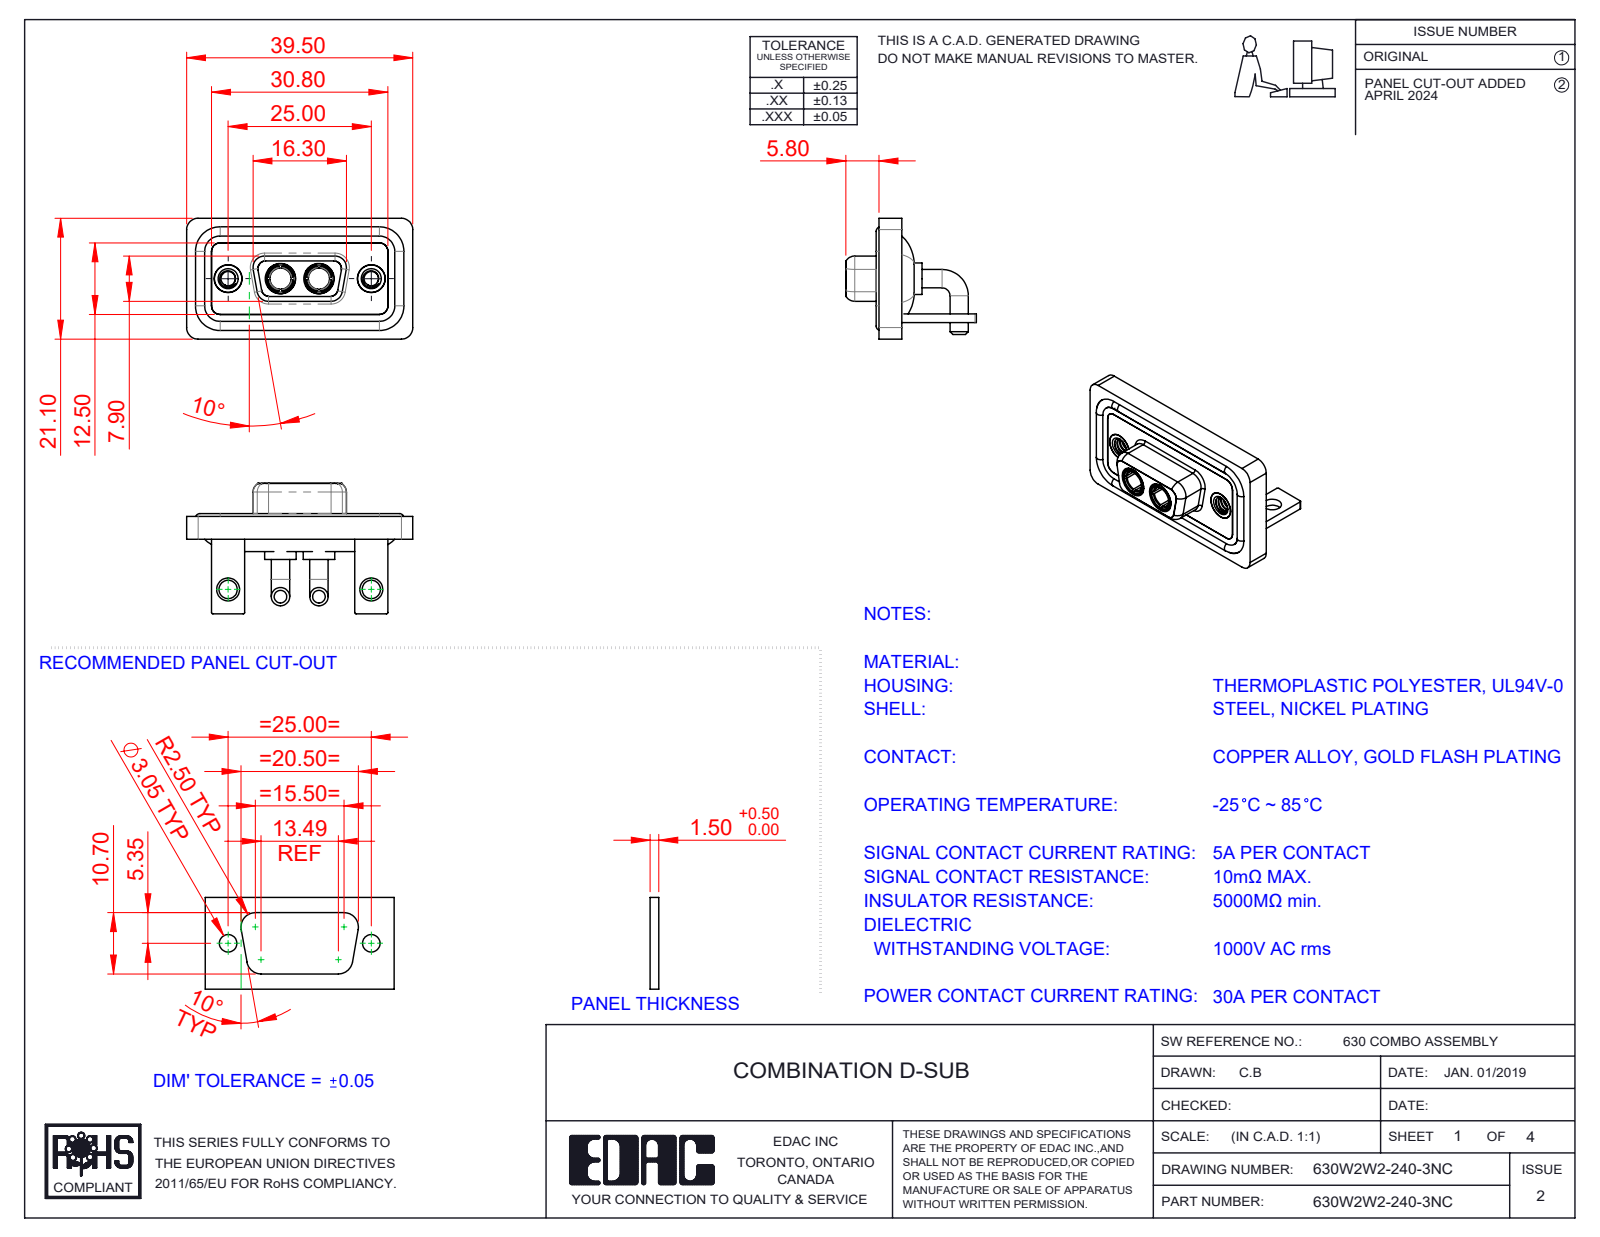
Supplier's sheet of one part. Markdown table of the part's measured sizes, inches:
| quantity | value |
| --- | --- |
| part name | 630Combo Shell Rear_09 Contacts; 630Combo Stabilizer Bracket_50 Contacts; 630Combo Waterproof Housing_09 Contacts; 630Combo Shell Front_09 Contacts (+4 more) |
| STEP written by | SolidWorks 2023 (CONFIG_CONTROL_DESIGN) |
| units | inches |
| bodies | 13 solids, 584 faces (183 planar, 260 cylindrical, 141 other) |
| overall size | 1.555 × 0.898 × 0.831 |
| volume | 0.319 in³ |
| surface area | 13.27 in² |
| round holes (diameter × count) | 0.191 × 4, 0.098 × 2, 0.126 × 2, 0.146 × 2, 0.157 × 2, 0.159 × 2, 0.197 × 2, 0.209 × 2 |
| round bosses / shafts (diameter × count) | 0.126 × 4, 0.063 × 4, 0.217 × 2, 0.205 × 2, 0.195 × 2, 0.195 × 2, 0.189 × 2, 0.187 × 2 |
| partial cylindrical surfaces (radius × count) | 0.079 × 19, 0.059 × 18, 0.01 × 16, 0.053 × 8, 0.063 × 8, 0.02 × 5, 0.024 × 4, 0.026 × 4 |
| main face-to-face distances | 0.016, 0.114, 0.059, 0.071, 0.043, 0.146, 0.031, 0.098, 0.063, 0.122 |
| hole center spacings | 0.36, 0.624, 0.984, 0.265 |
